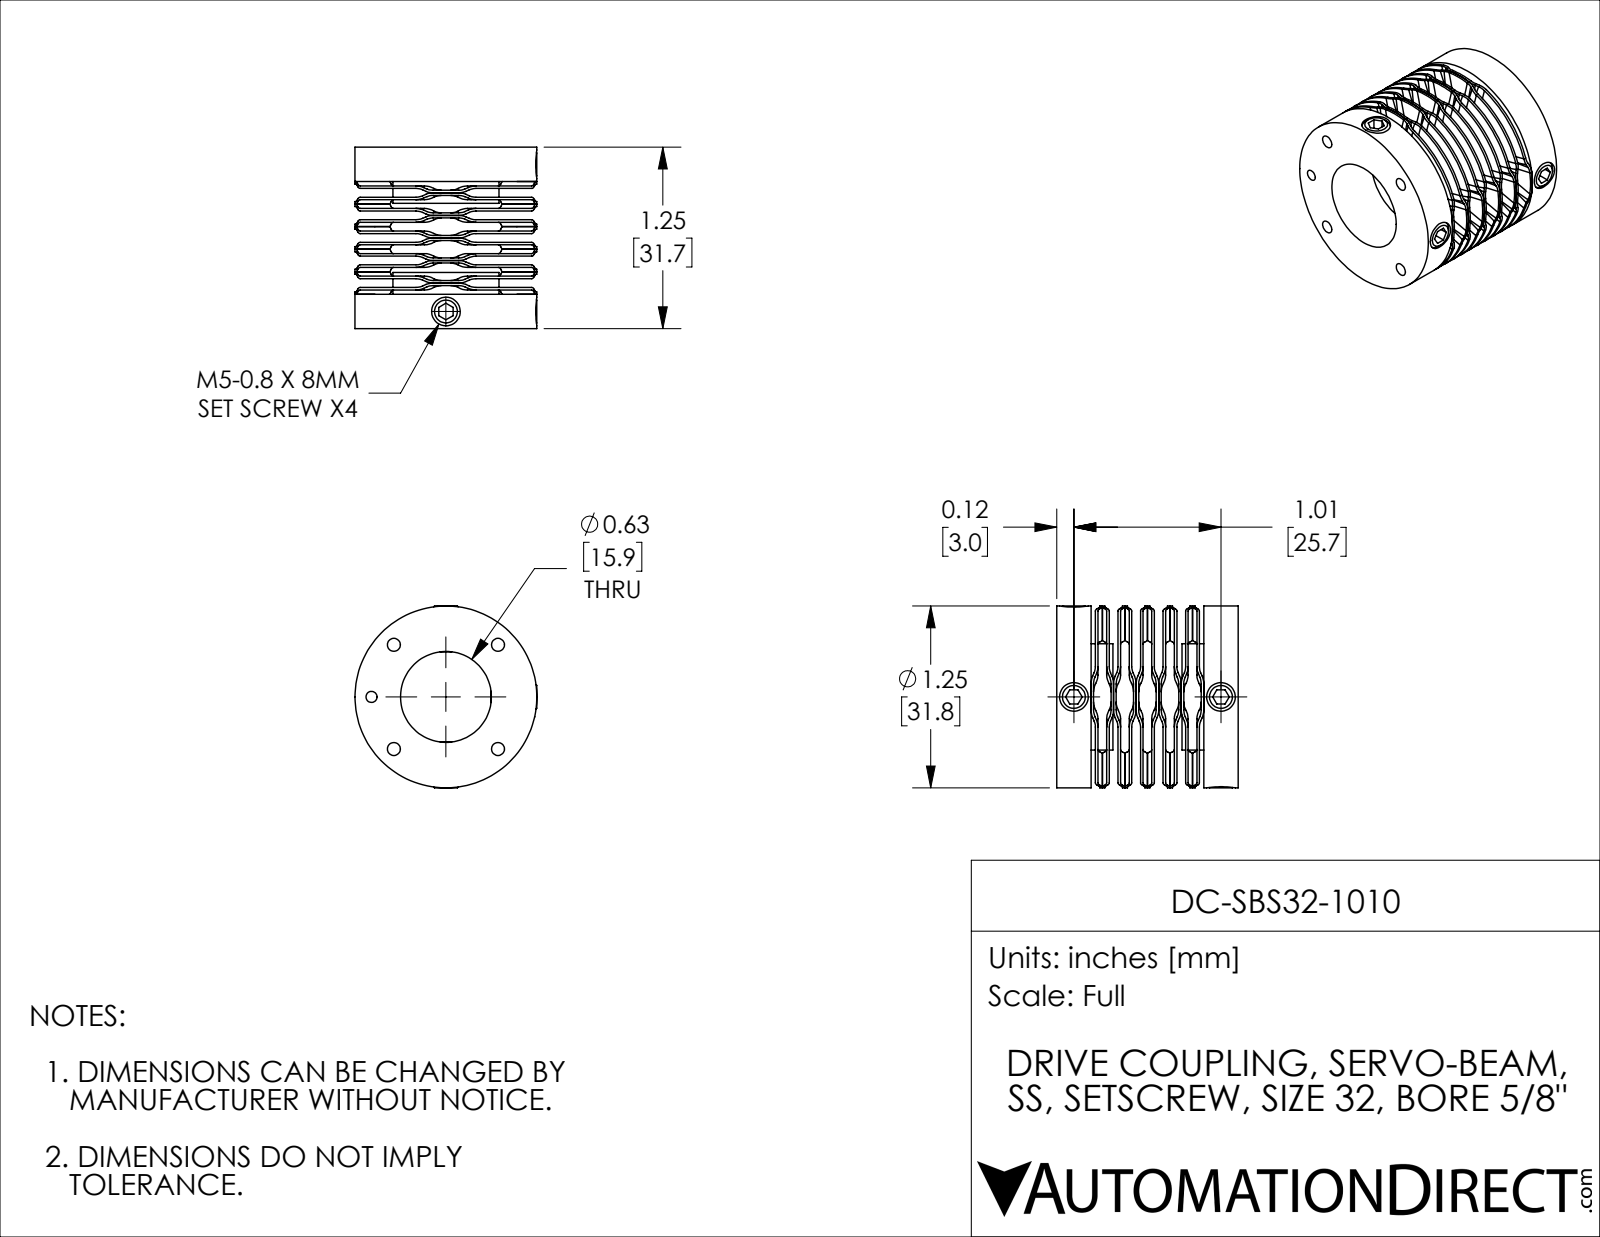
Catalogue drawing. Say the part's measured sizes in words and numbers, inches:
The part is named "DC-SBS32-1010". Its 3-D file was written by "SolidWorks 2019 (CONFIG_CONTROL_DESIGN)". It is 16 solids with 1196 faces: 202 planar, 178 cylindrical and 816 other. Overall it measures 1.25 by 1.25 by 1.247 inches. Its volume is 0.581 cubic inches and its surface area 26.14 square inches. Round holes: 4 of diameter 0.089, 4 of diameter 0.197, 1 of diameter 0.076, 1 of diameter 0.625. Round bosses or shafts: 1 of diameter 1.25, 1 of diameter 0.73. Partial cylindrical surfaces (rounded edges, fillets, slot ends): 1 of radius 0.391. The main face-to-face distances are 0.078, 0.155, 0.25, 0.095, 0.31, 0.172, 0.233, 0.387, 0.232, 0.236. The hole center spacings are 0.506, 0.716, 0.39, 0.941, 1.011, 1.012, 0.512.
